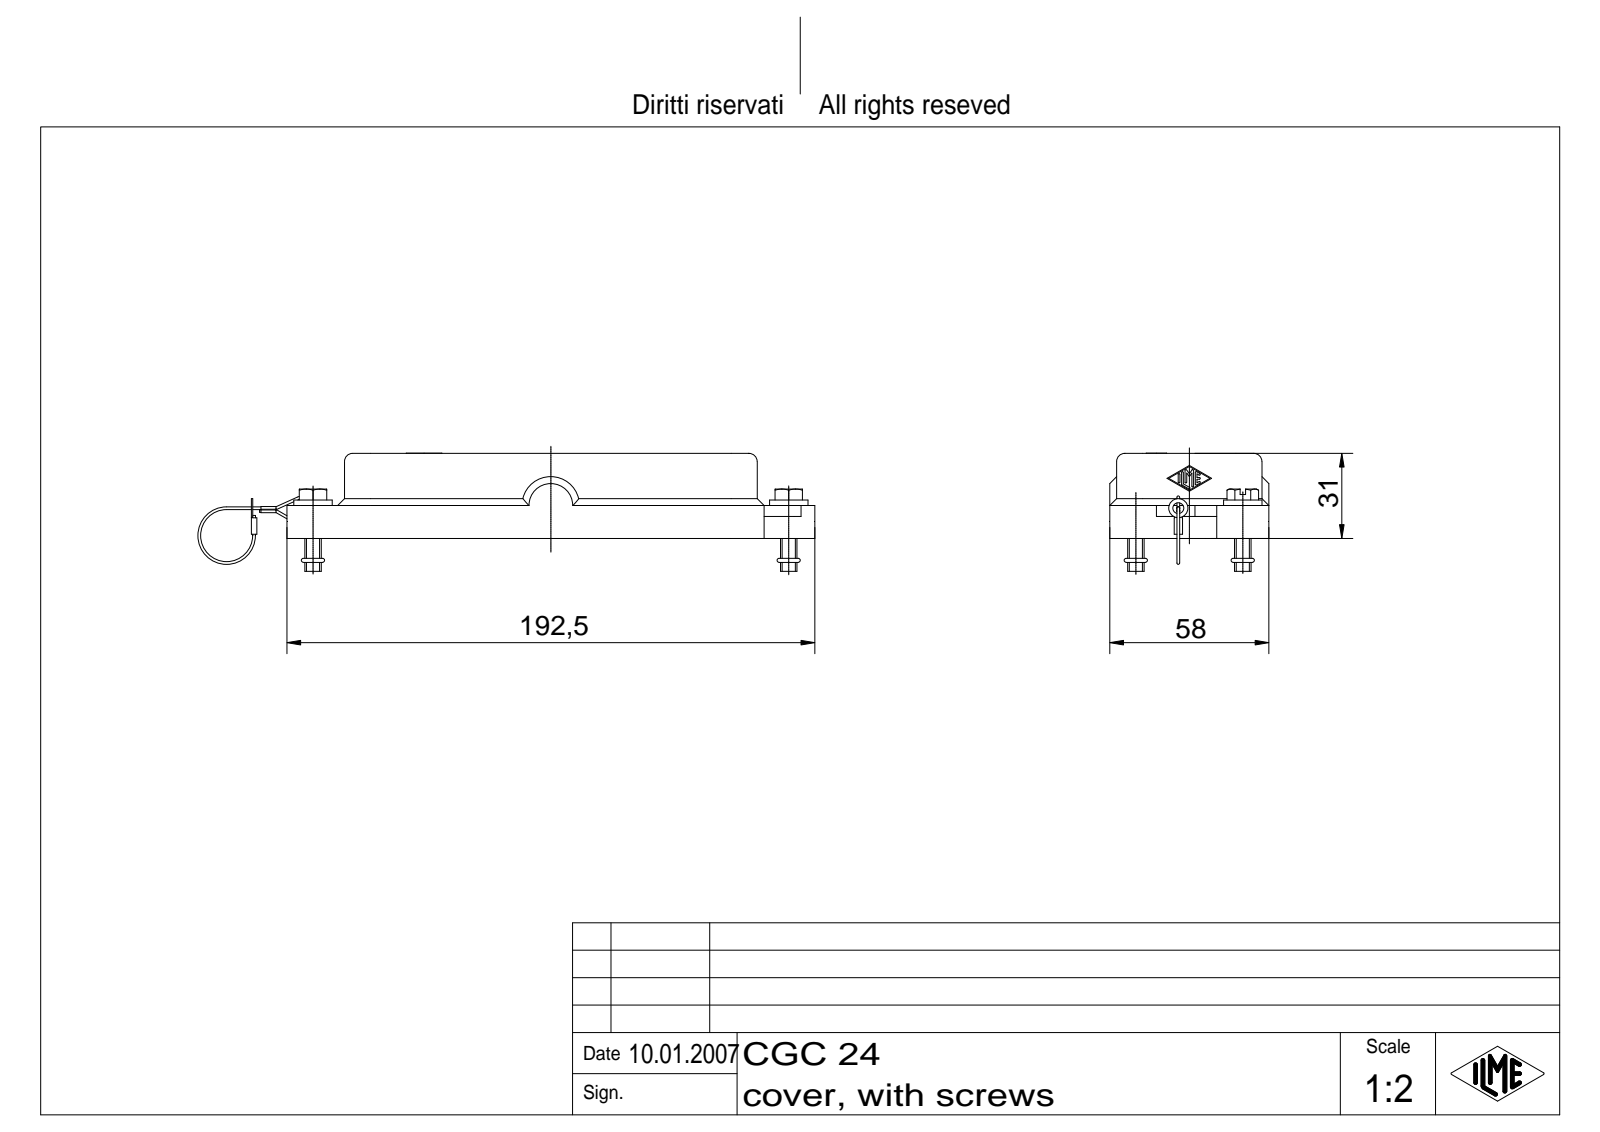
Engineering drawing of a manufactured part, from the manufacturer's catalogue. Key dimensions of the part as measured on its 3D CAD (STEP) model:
Part name (STEP PRODUCT): CGC 24
STEP written by: Autodesk Inventor 7 (AUTOMOTIVE_DESIGN)
Units: millimetres
Bodies: 2 solids, 272 faces (124 planar, 108 cylindrical, 40 other)
Overall size (bounding box): 225 × 58 × 43.1
Volume: 96 240 mm³ · Surface area: 44 406 mm²
Round holes (diameter × count): ⌀3 ×2, ⌀7 ×2, ⌀14 ×2, ⌀4 ×1
Round bosses / shafts (diameter × count): ⌀1 ×5, ⌀6 ×2, ⌀5.5 ×2, ⌀7 ×1
Partial cylindrical surfaces — rounded edges, fillets, slot ends (radius × count): R0.25 ×14, R3 ×4, R5 ×4, R7 ×4, R9.5 ×4, R0.62 ×2, R1 ×2, R4 ×2
Main face-to-face distances: 7, 3, 2.5, 5.5, 55.5, 52.5, 50, 53, 47, 58
Hole centre spacings: 23.55, 172.7, 170.69, 177.83
